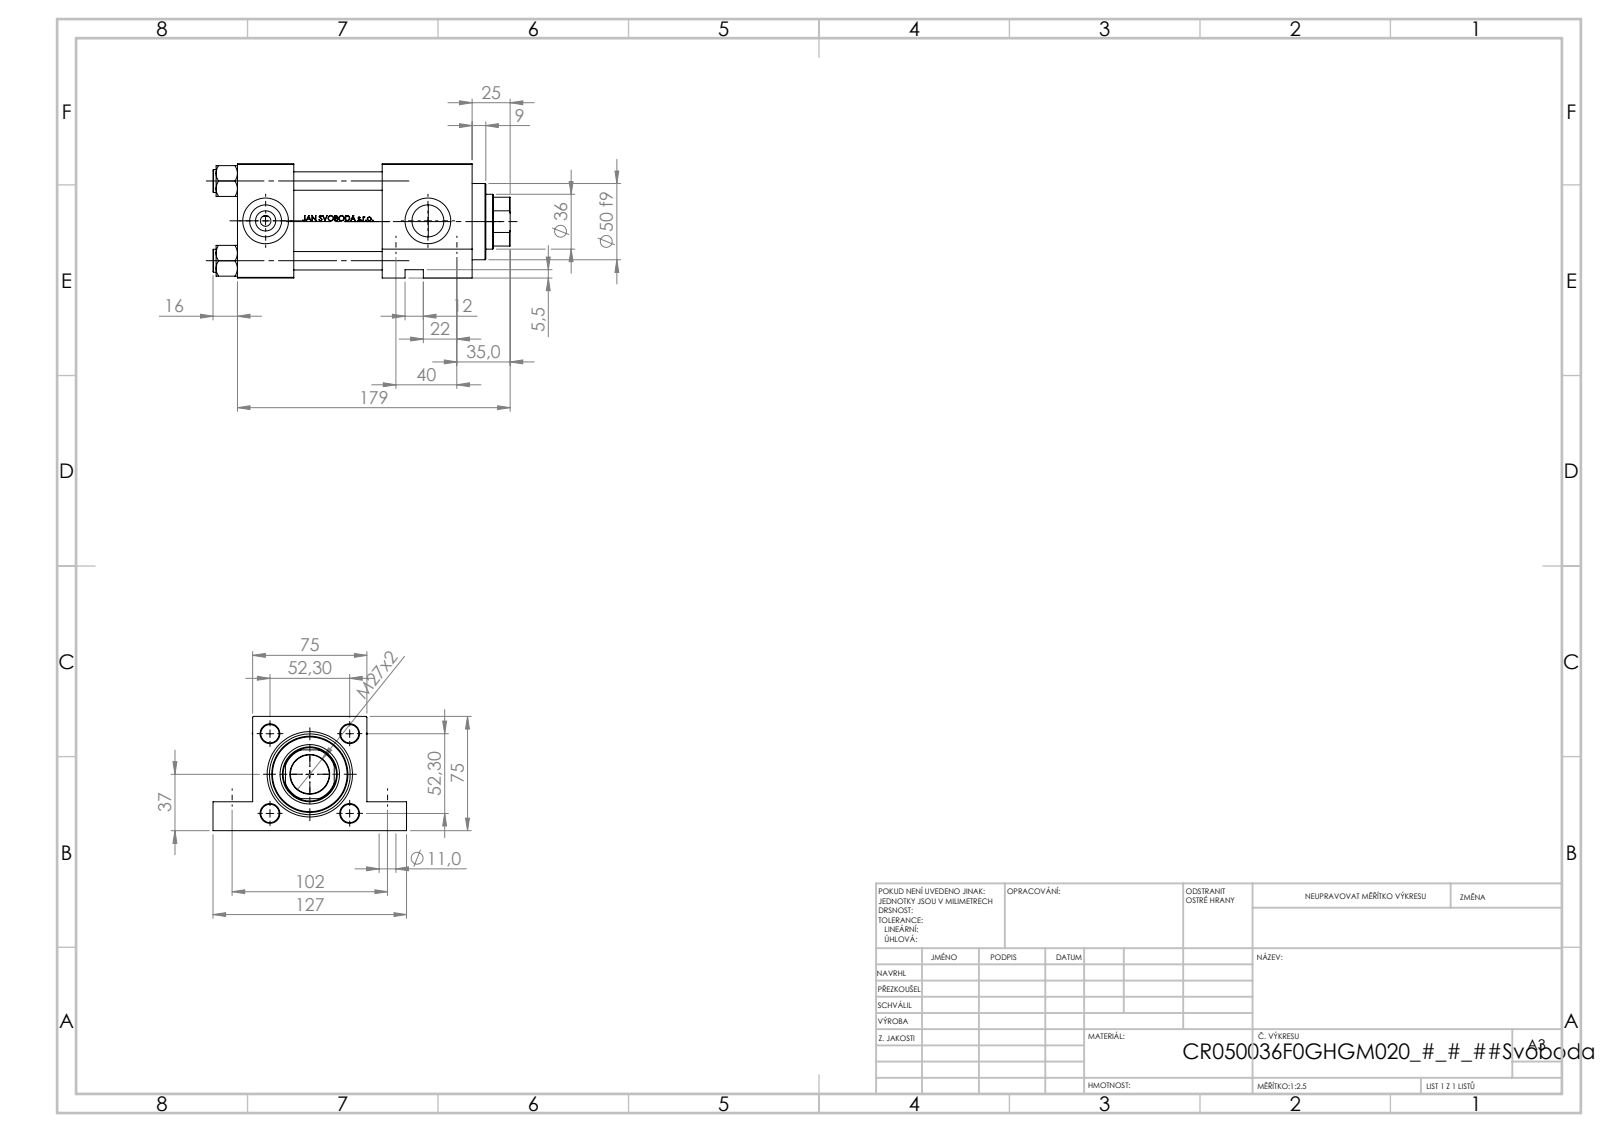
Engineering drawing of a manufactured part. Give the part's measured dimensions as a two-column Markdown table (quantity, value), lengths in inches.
| quantity | value |
| --- | --- |
| part name | V215CR_VCP_F; NUT_M5_F; V215_VC_A; V215CR_F_Body (+1 more) |
| STEP written by | SolidWorks 2019 (CONFIG_CONTROL_DESIGN) |
| units | inches |
| bodies | 11 solids, 1103 faces (437 planar, 126 cylindrical, 540 other) |
| overall size | 7.677 × 5 × 2.953 |
| volume | 44.89 in³ |
| surface area | 254.7 in² |
| round holes (diameter × count) | 0.472 × 4, 0.276 × 2, 0.433 × 2, 0.433 × 2, 0.825 × 2, 1.181 × 2, 1.004 × 1, 1.417 × 1, 1.535 × 1, 1.614 × 1, 2.087 × 1 |
| round bosses / shafts (diameter × count) | 0.591 × 4, 2.205 × 1, 1.969 × 1 |
| partial cylindrical surfaces (radius × count) | 0.689 × 1 |
| main face-to-face distances | 2.953, 1.457, 2.283, 3.74, 4.606, 6.063, 2.323, 0.748, 2.205, 1.024 |
| hole center spacings | 2.059, 1.442, 1.47, 1.575, 2.912, 4.016, 4.313, 4.193 |
